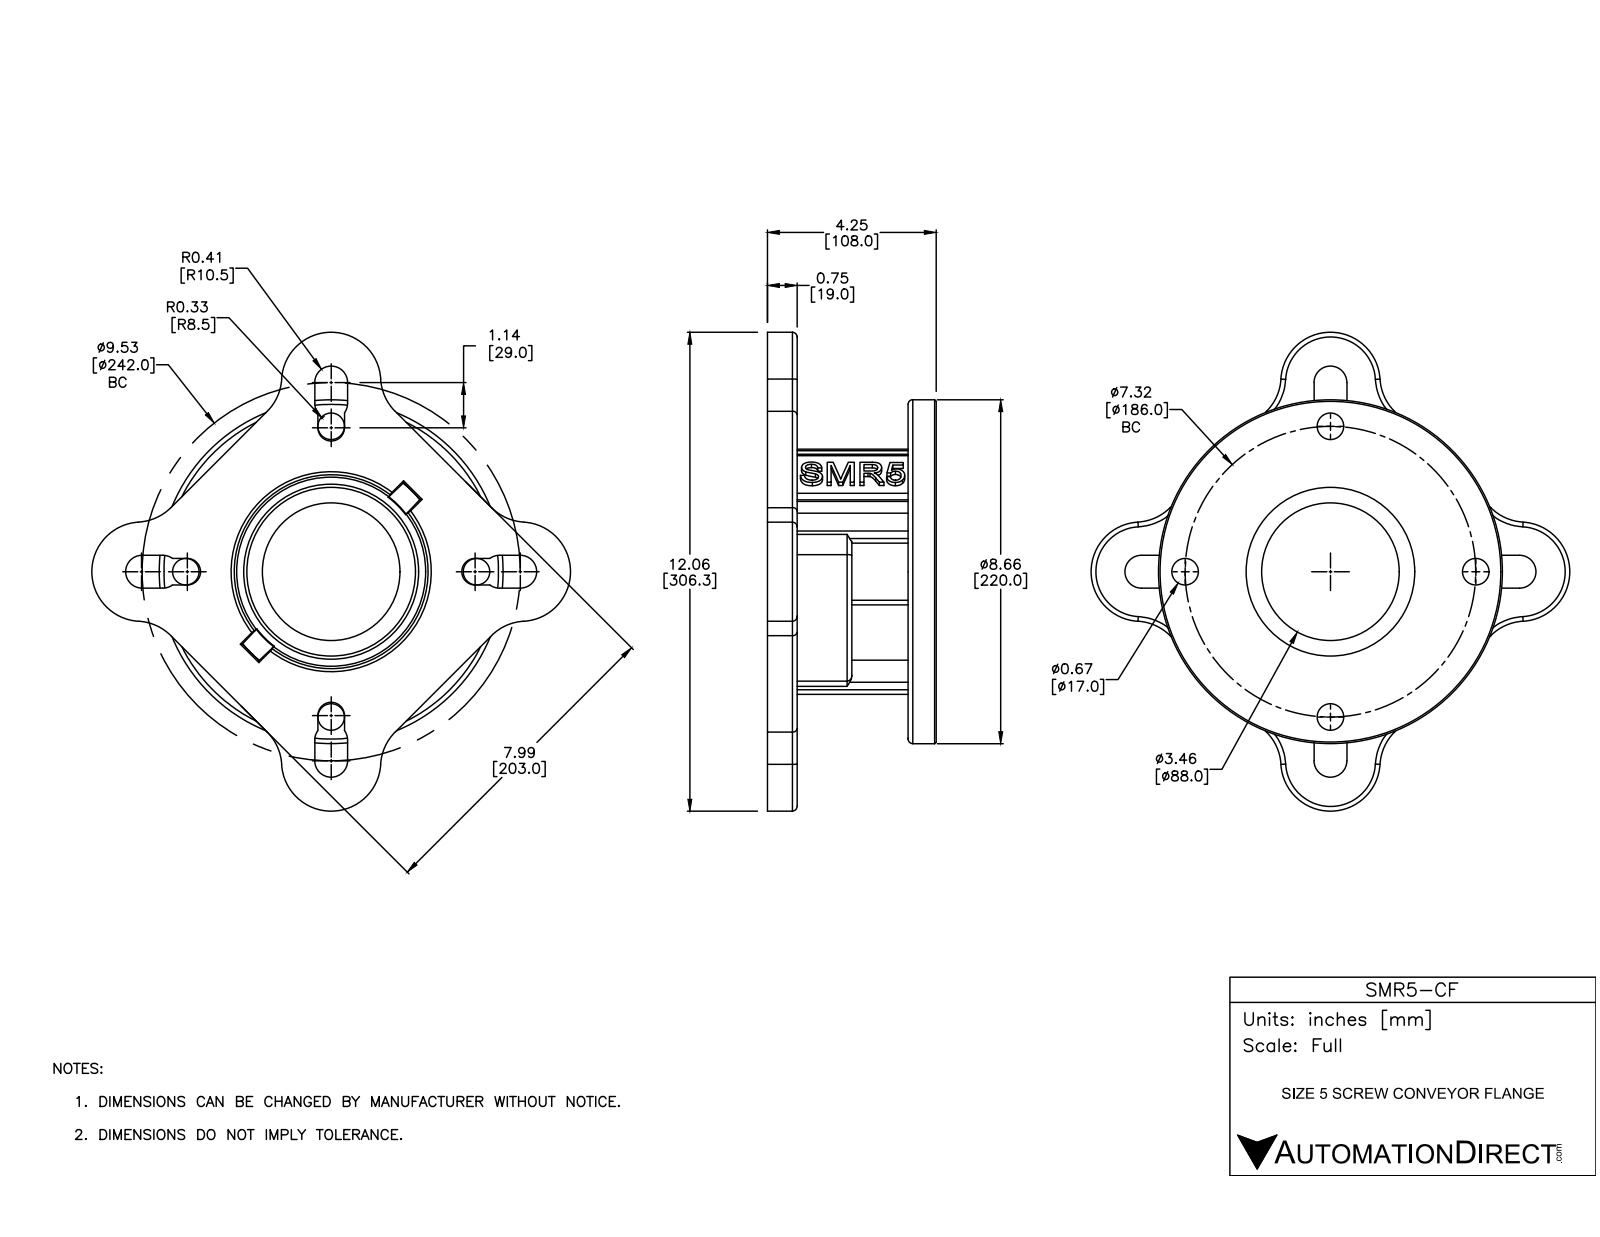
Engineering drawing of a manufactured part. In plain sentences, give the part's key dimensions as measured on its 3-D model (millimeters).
The part is named "SMR5-CF". Its 3-D file was written by "SolidWorks 2016 (AUTOMOTIVE_DESIGN)". It is 1 solid with 232 faces: 87 planar, 80 cylindrical and 65 other. Overall it measures 306.3 by 306.3 by 108 millimeters. Its volume is 1 613 000 cubic millimeters and its surface area 216 700 square millimeters. Round holes: 4 of diameter 17, 1 of diameter 88, 1 of diameter 108, 1 of diameter 124. Round bosses or shafts: 1 of diameter 220. Partial cylindrical surfaces (rounded edges, fillets, slot ends): 12 of radius 31.8, 8 of radius 3, 8 of radius 10, 8 of radius 10.5, 4 of radius 8.5, 4 of radius 15, 1 of radius 70, 1 of radius 86. The main face-to-face distances are 108, 19, 89, 18, 71, 90, 54, 36, 35, 33. The hole center spacings are 93, 131.5, 186.
